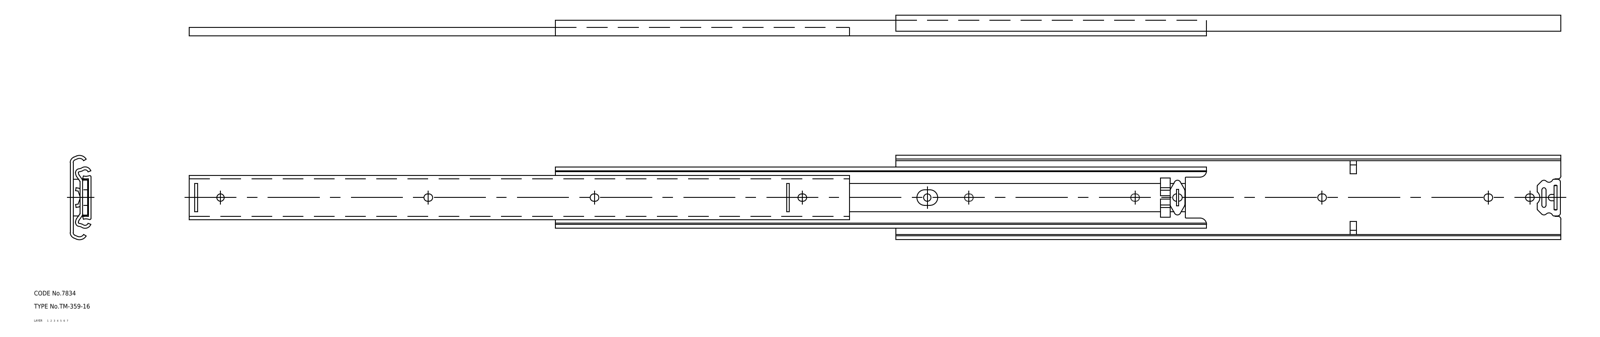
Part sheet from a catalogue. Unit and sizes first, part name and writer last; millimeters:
Units: millimetres
Overall size (bounding box): 838.4 × 51.5 × 12.8
Round holes (diameter × count): ⌀4.5 ×3
Partial cylindrical surfaces — rounded edges, fillets, slot ends (radius × count): R2.25 ×16, R2 ×11, R4.75 ×6, R0.45 ×4, R0.5 ×4, R0.6 ×4, R0.3 ×2, R0.77 ×2
Main face-to-face distances: 1.8, 5.91, 12.7, 10.9, 9.3, 11.1, 1.6, 4.11, 5.19, 6.79
Hole centre spacings: 202.2, 229.8, 432
Volume: 106 780 mm³ · Surface area: 124 653 mm²
Bodies: 3 solids, 233 faces (128 planar, 105 cylindrical, 0 other)
Part name (STEP PRODUCT): member_C; member_B; TM_359_16; member_A
STEP written by: SolidWorks 2015 (AUTOMOTIVE_DESIGN)
